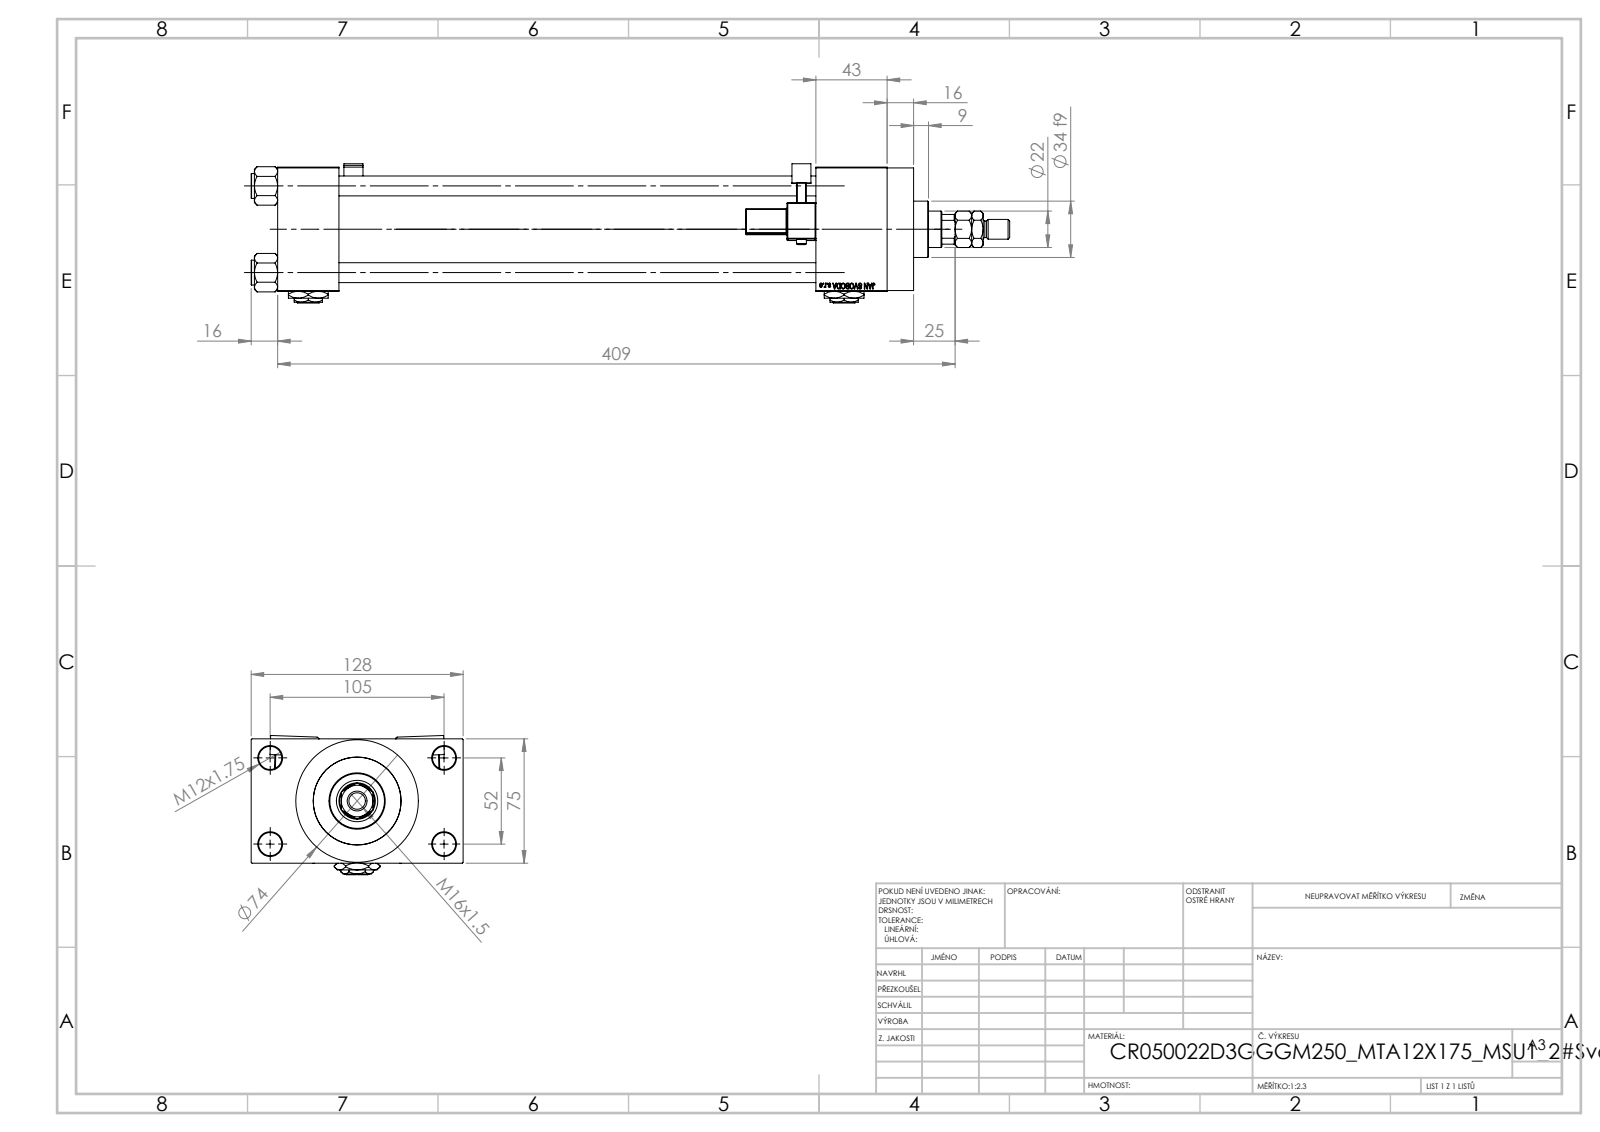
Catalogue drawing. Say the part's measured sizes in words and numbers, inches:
The part is named "V215CR_VCP_D; V215_VC_A; V215CR_D_Body; V215CR_MSU (+4 more)". Its 3-D file was written by "SolidWorks 2019 (CONFIG_CONTROL_DESIGN)". It is 16 solids with 1408 faces: 618 planar, 164 cylindrical and 626 other. Overall it measures 18.031 by 5.039 by 3.308 inches. Its volume is 70.6 cubic inches and its surface area 482 square inches. Round holes: 4 of diameter 0.472, 4 of diameter 0.551, 2 of diameter 0.276, 2 of diameter 0.825, 2 of diameter 1.181, 1 of diameter 0.413, 1 of diameter 0.866, 1 of diameter 0.984, 1 of diameter 1.614, 1 of diameter 1.969, 1 of diameter 2.087. Round bosses or shafts: 4 of diameter 0.591, 2 of diameter 0.236, 1 of diameter 2.913, 1 of diameter 2.205, 1 of diameter 1.339, 1 of diameter 0.472, 1 of diameter 0.394. Partial cylindrical surfaces (rounded edges, fillets, slot ends): 48 of radius 0.02, 2 of radius 0.039, 2 of radius 0.098, 2 of radius 0.157, 1 of radius 0.413. The main face-to-face distances are 2.953, 11.339, 3.996, 1.457, 12.795, 1.043, 14.488, 13.031, 1.693, 0.63. The hole center spacings are 1.037, 1.456, 2.059, 2.3, 2.307, 3.096, 3.715, 2.047.
